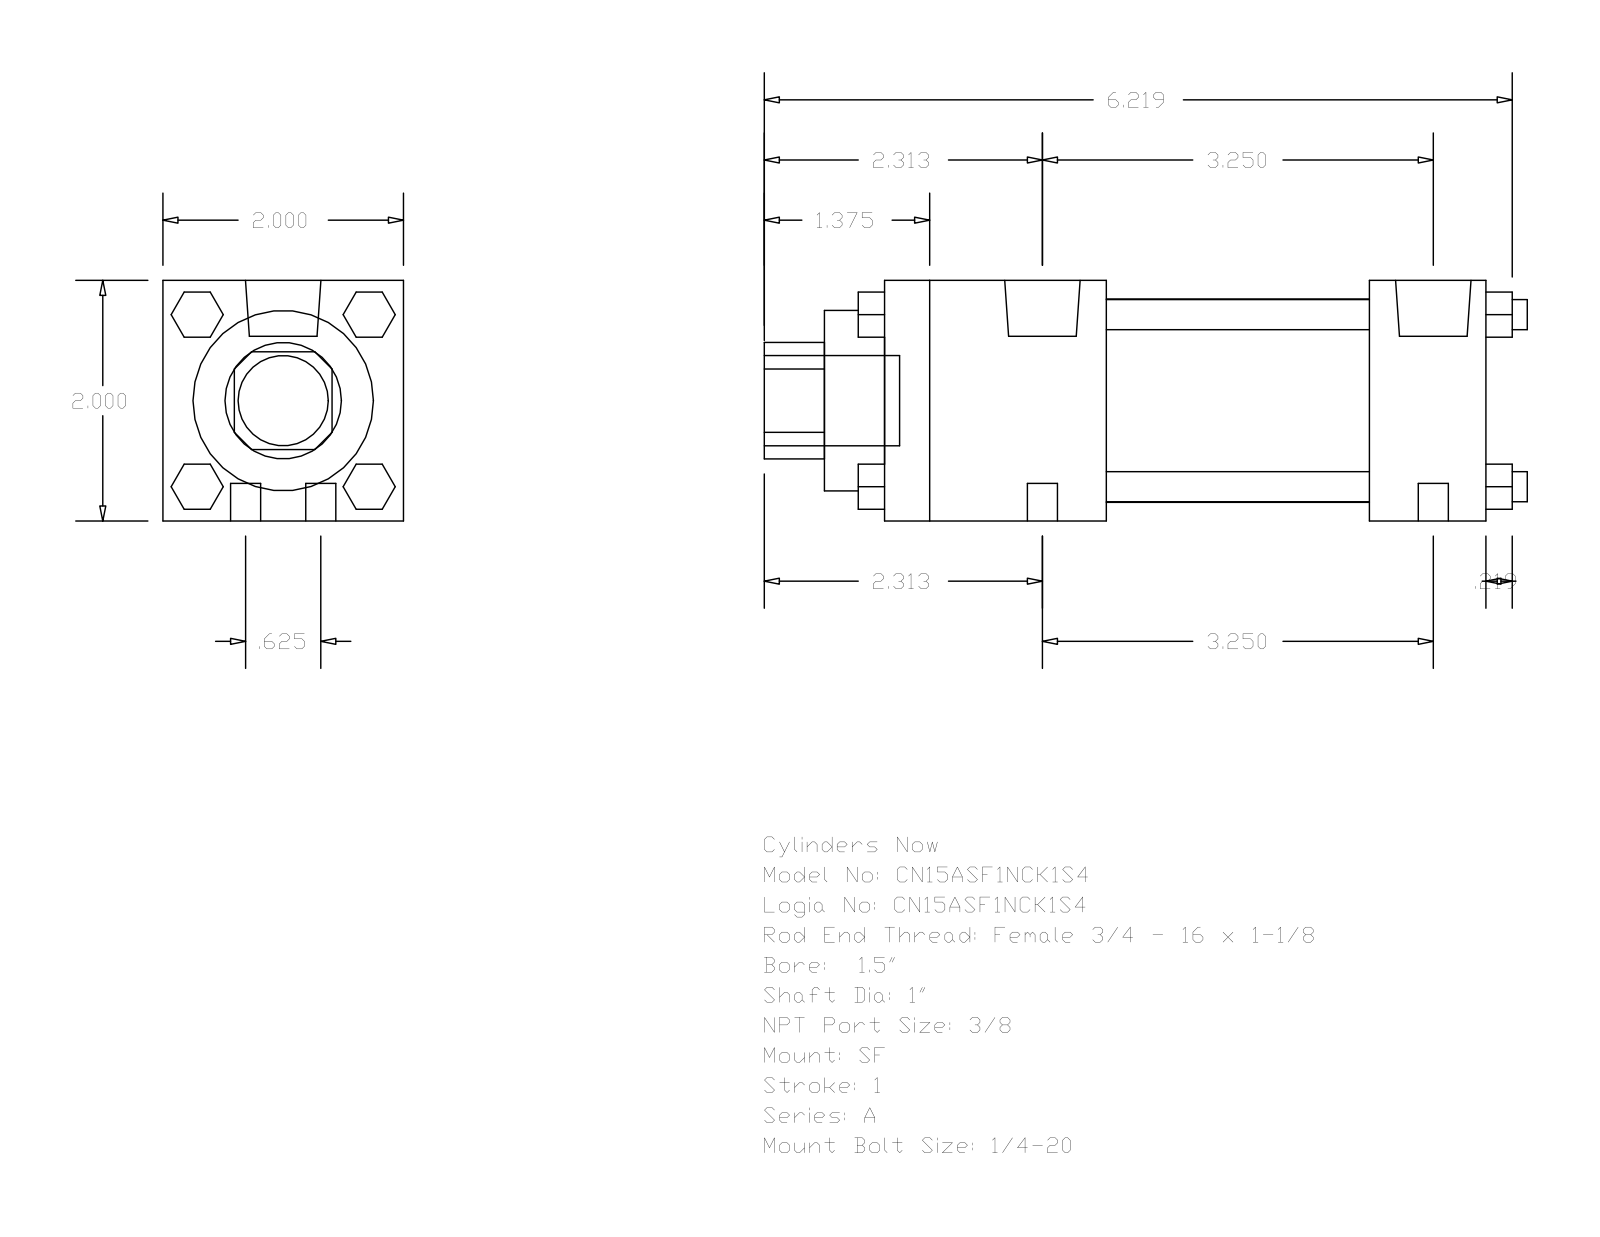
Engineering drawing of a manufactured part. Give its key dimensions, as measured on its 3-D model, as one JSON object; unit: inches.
{"part_name": "A_SF__0150_1", "step_written_by": "GSSL Pune (CONFIG_CONTROL_DESIGN)", "units": "inches", "bodies": {"solids": 0, "faces": 124, "planar": 94, "cylindrical": 30, "other": 0}, "overall_size": [6.344, 2, 2], "round_holes": [[1, 1], [1.5, 1], [1.69, 1]], "round_bosses_or_shafts": [[0.25, 8], [0.627, 2], [0.219, 2], [0.75, 1]], "partial_cylinders_radius": [[0.484, 1]], "face_to_face_distances": [2, 5, 1.844, 4.031, 2.187, 3.156, 0.969, 0.5, 2.344, 4.531]}
